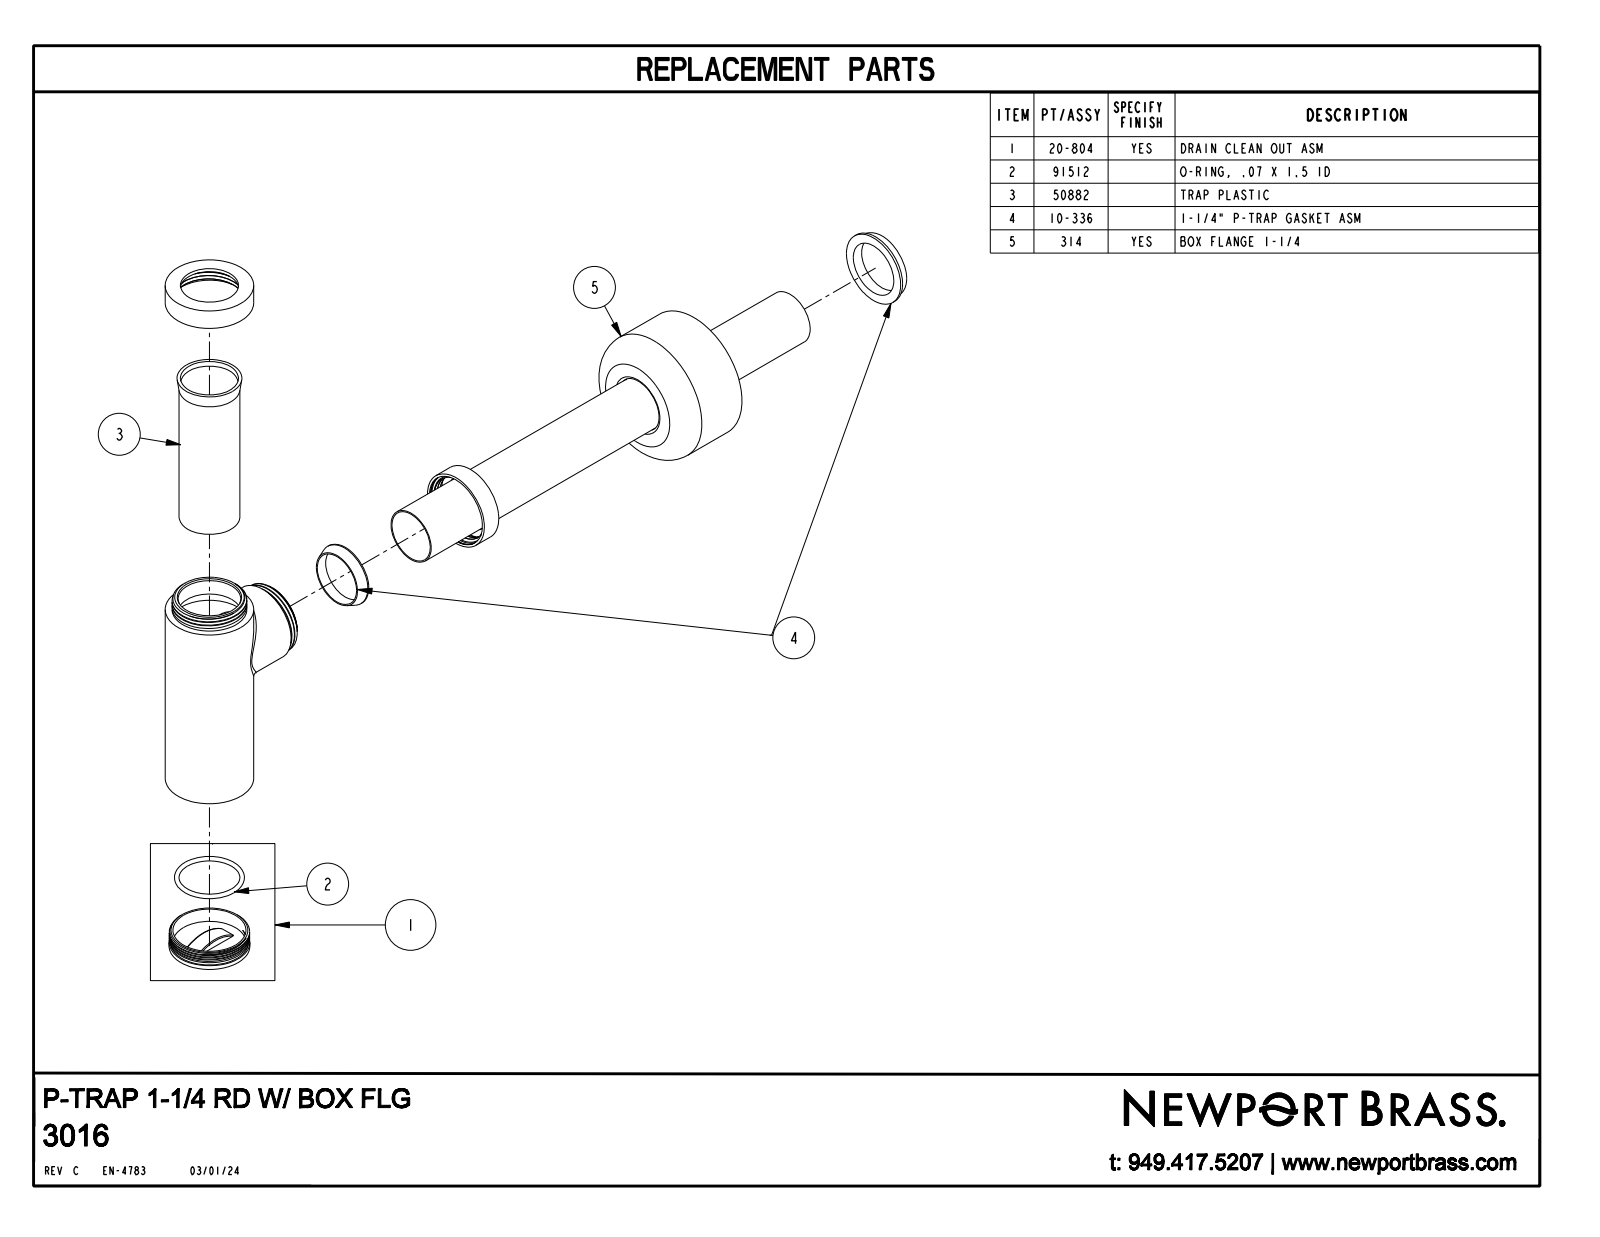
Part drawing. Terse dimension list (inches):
name: 3016
written by: CREO PARAMETRIC BY PTC INC, 2018500 (CONFIG_CONTROL_DESIGN)
unit: in
bodies: 2 solids, 227 faces (72 planar, 104 cylindrical, 51 other)
size: 14.007 × 5.06 × 3
volume: 25.07 in³; area: 333.8 in²
holes: 2× ⌀1.19, 2× ⌀1.26, 1× ⌀1.128, 1× ⌀1.23, 1× ⌀1.27, 1× ⌀1.28, 1× ⌀1.73, 1× ⌀1.85, 1× ⌀2.52, 1× ⌀2.954
bosses: 2× ⌀1.25, 1× ⌀3, 1× ⌀2.56, 1× ⌀1.95, 1× ⌀1.78, 1× ⌀1.77, 1× ⌀1.75, 1× ⌀1.715
rounds: 12× R0.07, 2× R0.1, 1× R0.825, 1× R0.825, 1× R0.98, 1× R1.02
face distances: 0.1, 0.02, 4.9, 4.96, 5.06, 7.9, 7.88, 0.45, 0.06, 5
